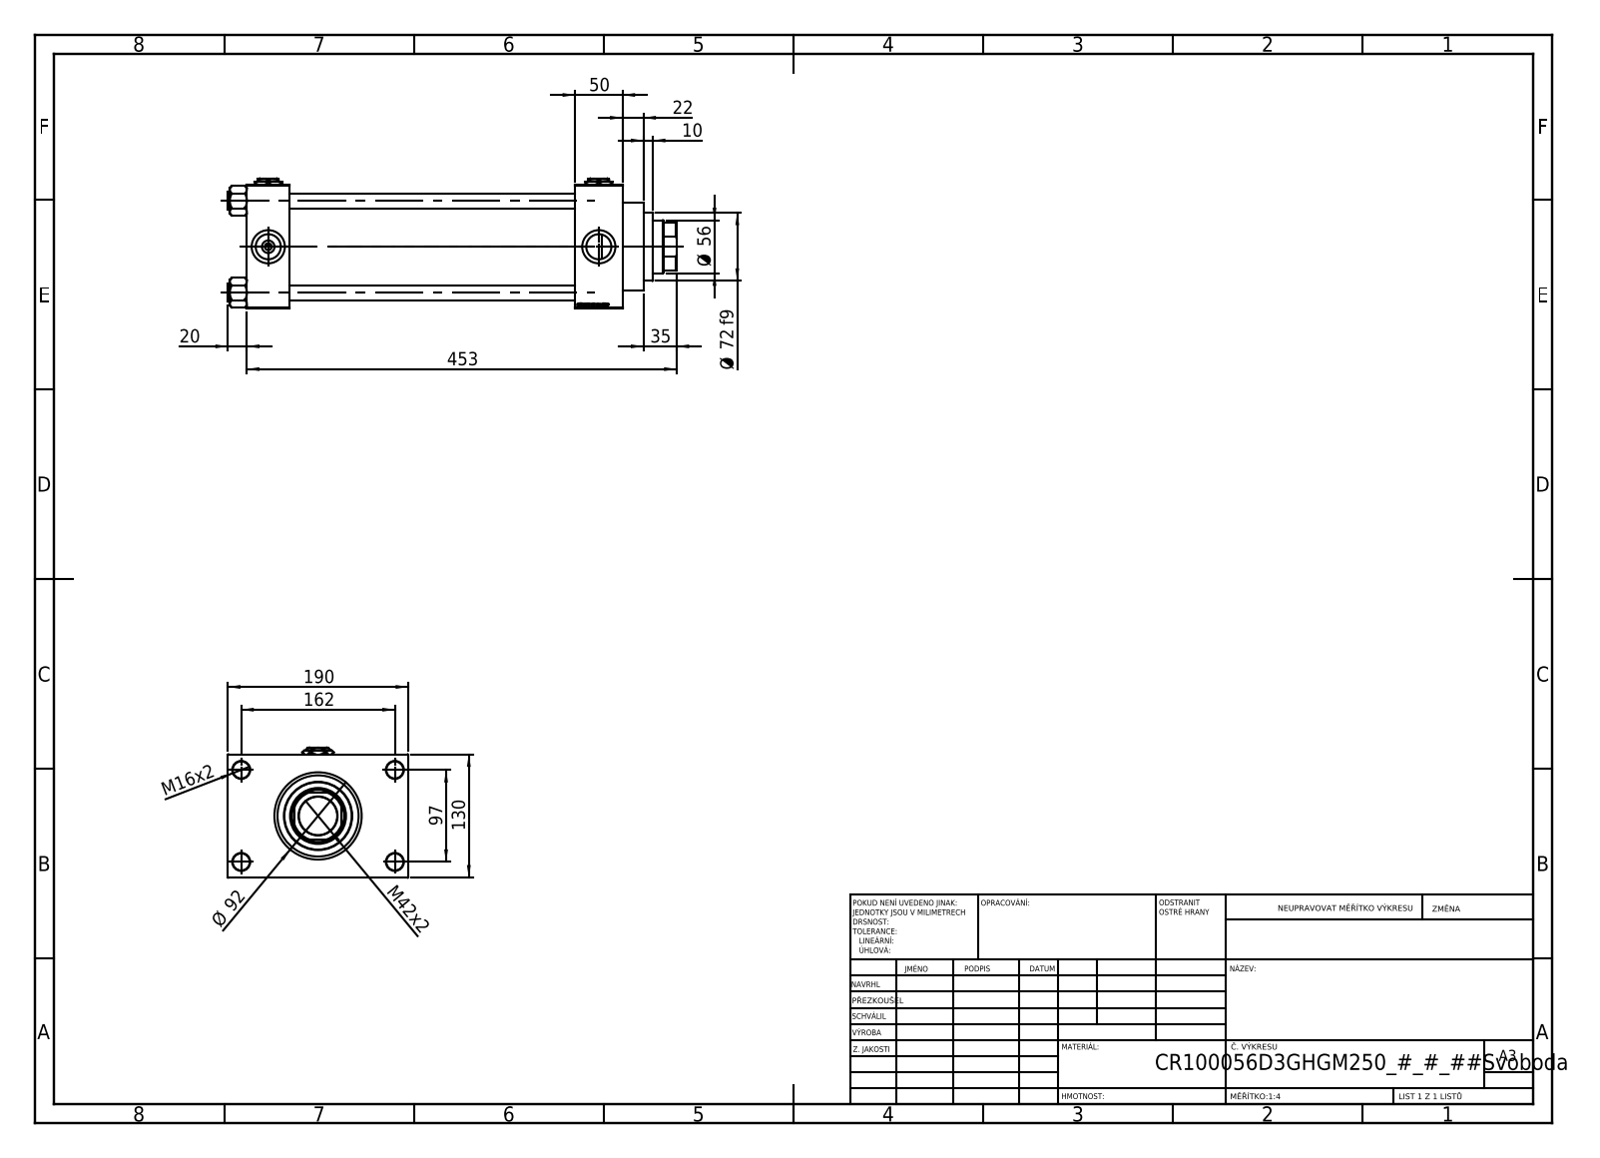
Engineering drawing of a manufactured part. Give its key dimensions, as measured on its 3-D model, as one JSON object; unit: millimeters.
{"part_name": "V215CR_D_Body; V215_VC_A; NUT_M5_D; V215CR_D_TYCINKA (+2 more)", "step_written_by": "SolidWorks 2019 (CONFIG_CONTROL_DESIGN)", "units": "millimeters", "bodies": {"solids": 13, "faces": 1252, "planar": 593, "cylindrical": 99, "other": 560}, "overall_size": [473, 190, 137], "volume_mm3": 3588000, "surface_area_mm2": 604838, "round_holes": [[16, 4], [18, 4], [26.44, 4], [35, 4], [7, 3], [40.5, 1], [56, 1], [59, 1], [76, 1], [85.5, 1], [100, 1]], "round_bosses_or_shafts": [[19, 4], [106, 1], [92, 1], [72, 1]], "partial_cylinders_radius": [[27, 1]], "face_to_face_distances": [130, 50, 45, 346, 301, 351, 396, 30, 160, 190], "hole_center_spacings": [32.55, 68.52, 94.41, 96.9, 102.27, 129.45, 161.73, 97]}
